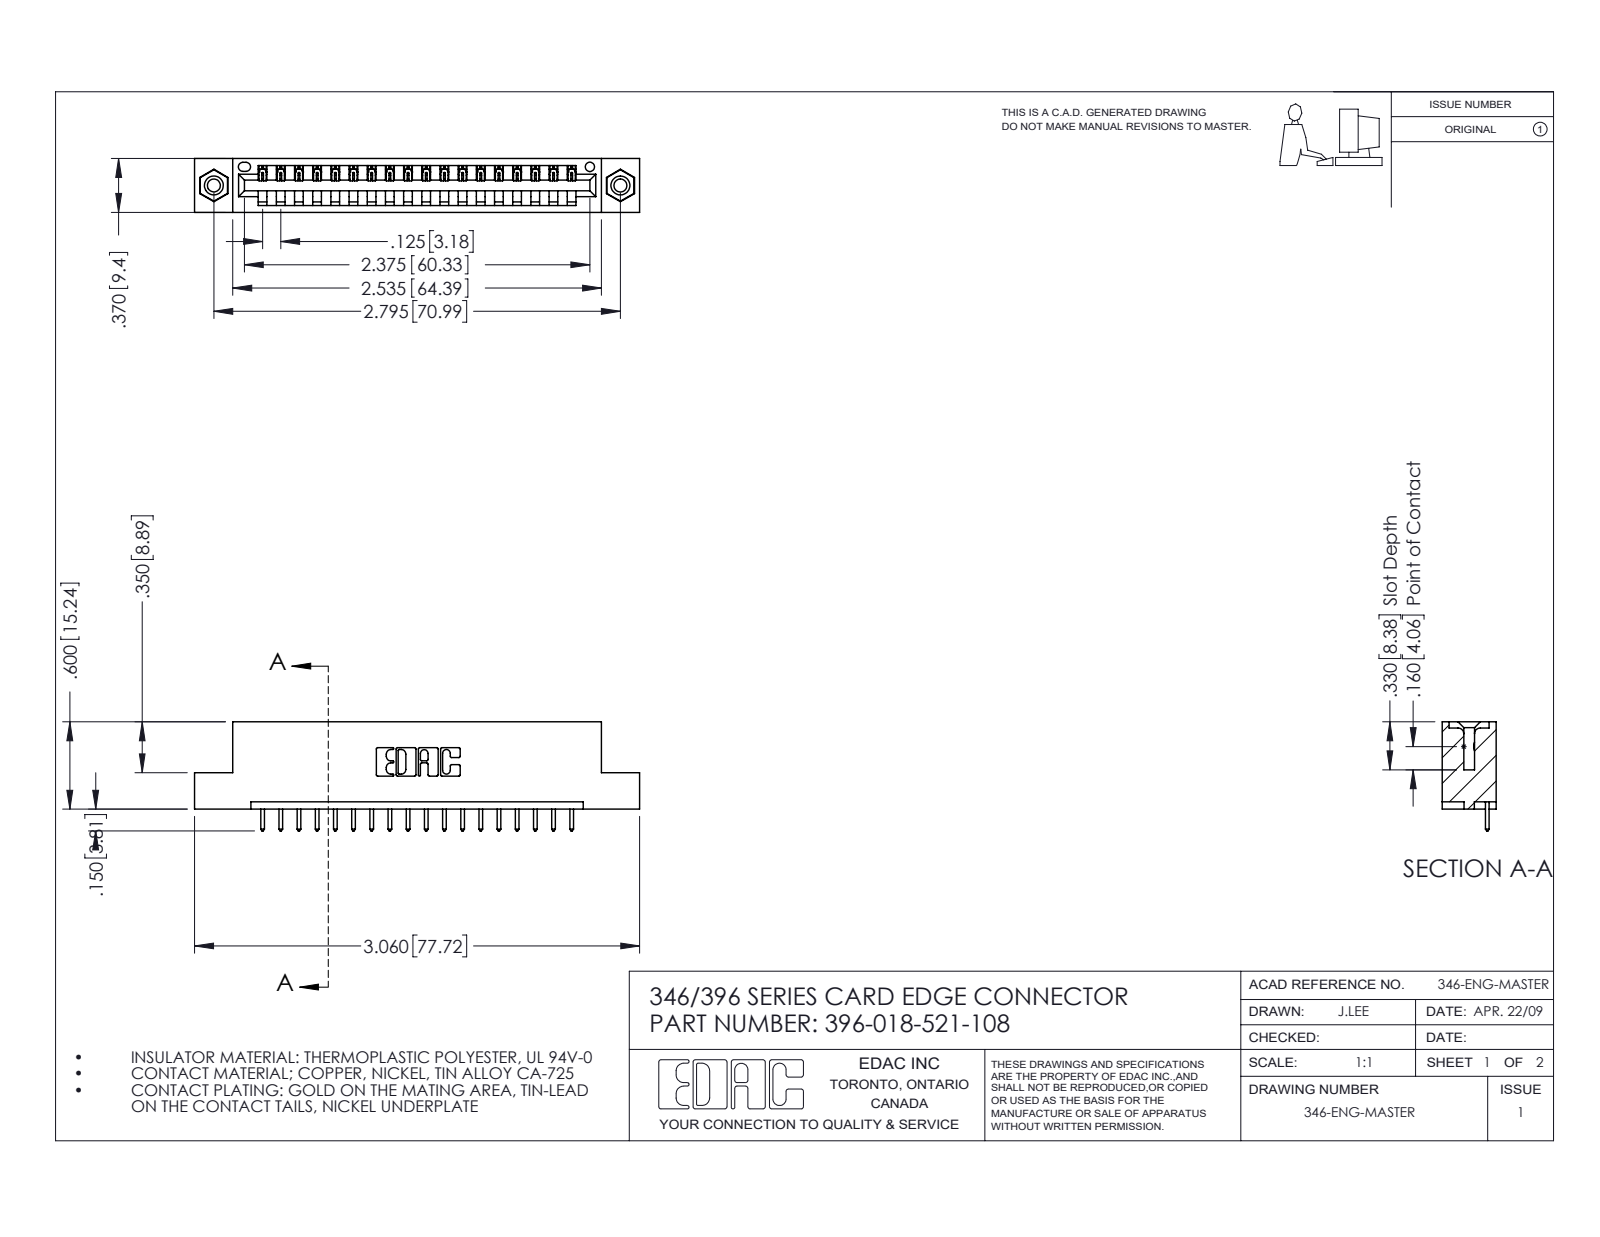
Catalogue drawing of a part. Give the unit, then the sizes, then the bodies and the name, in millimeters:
Units: millimetres
Overall size (bounding box): 77.7 × 19.1 × 9.4
Round holes (diameter × count): ⌀2.3 ×2, ⌀3.2 ×2, ⌀4 ×2, ⌀1.6 ×1
Round bosses / shafts (diameter × count): ⌀3.9 ×2
Partial cylindrical surfaces — rounded edges, fillets, slot ends (radius × count): R0.2 ×36, R0.3 ×36, R0.3 ×22, R0.2 ×6, R0.8 ×6, R0.7 ×3, R0.8 ×2, R1 ×2
Main face-to-face distances: 1.2, 8.2, 9.4, 6.4, 1.8, 7.6, 0.6, 3.8, 5.6, 2.5
Hole centre spacings: 6.2, 65.7, 71
Volume: 7 210 mm³ · Surface area: 8 581 mm²
Bodies: 21 solids, 1226 faces (828 planar, 382 cylindrical, 16 other)
Part name (STEP PRODUCT): 396-018-521-108; 345-292-001_345-293-121; 345-250-001_345-250-003-102; 346 Part_Flush Mounting Lugs - 0.156 Dia-TI
STEP written by: SolidWorks 2016 (CONFIG_CONTROL_DESIGN)
